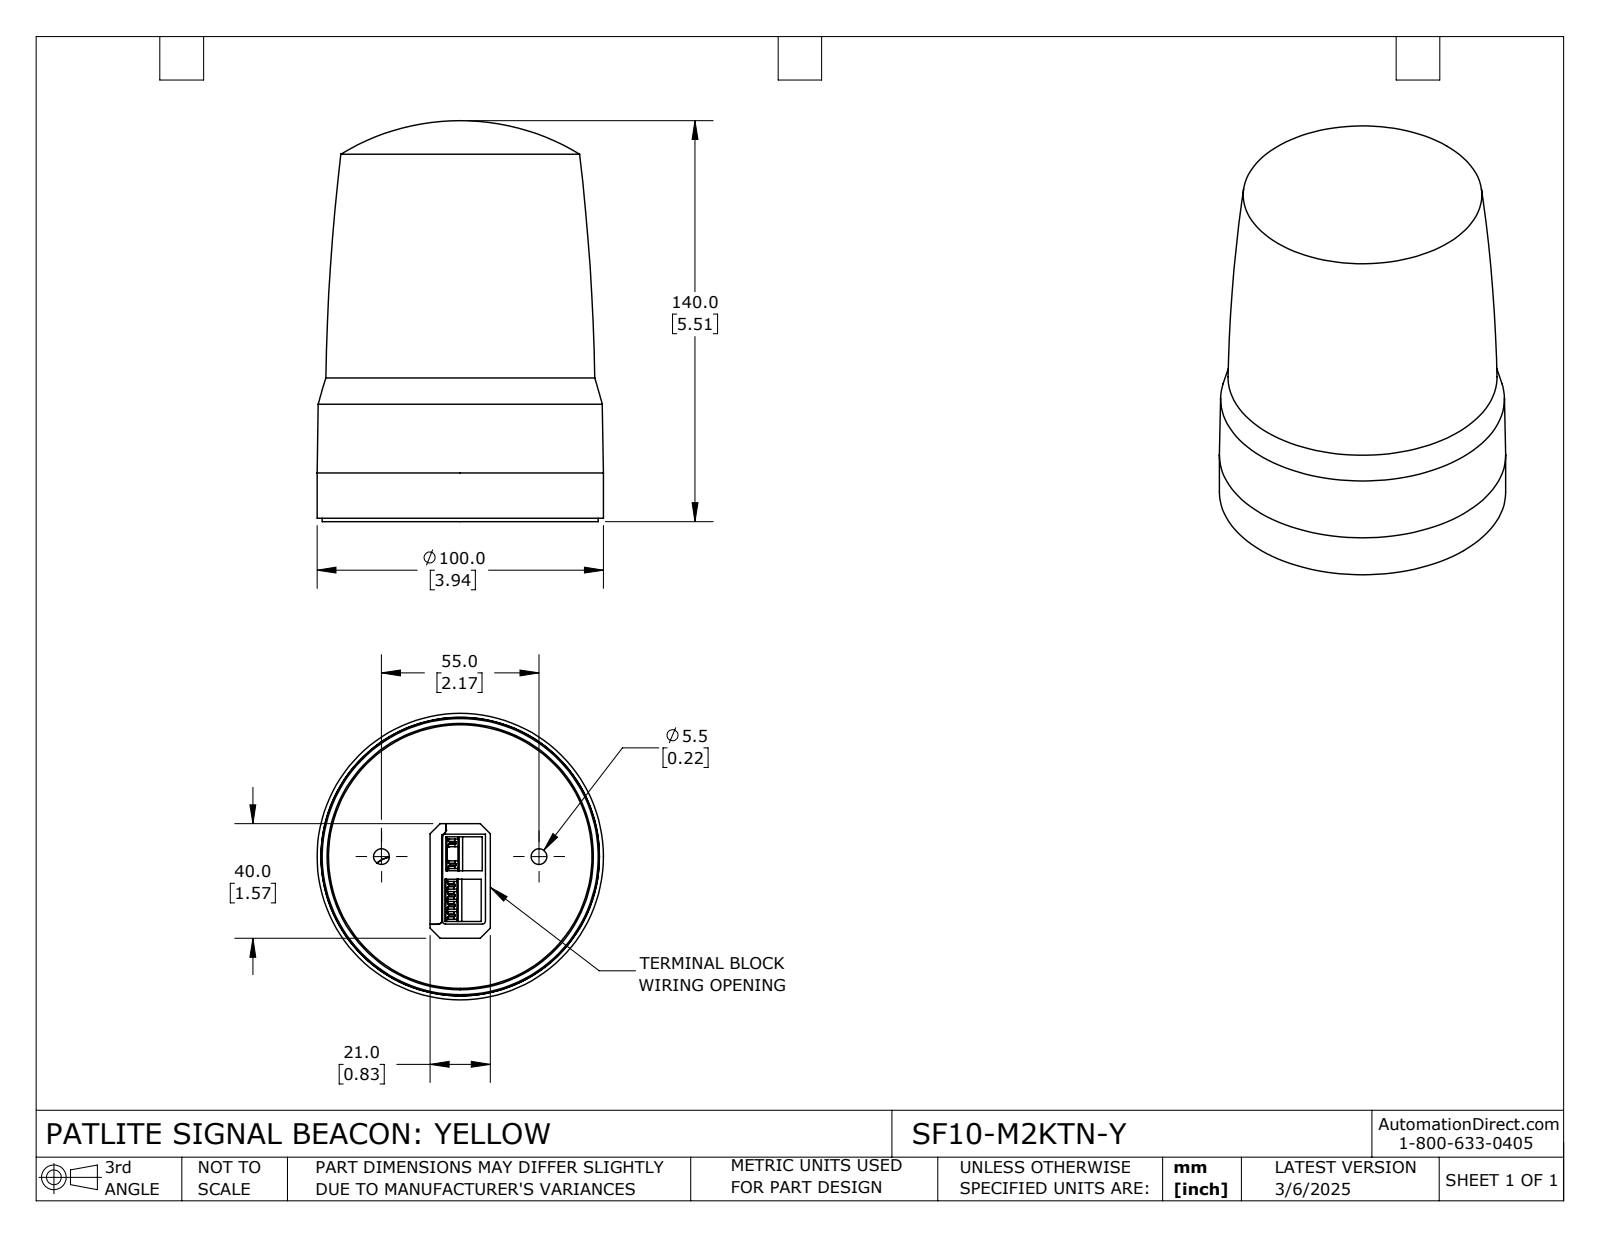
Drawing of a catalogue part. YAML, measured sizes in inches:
part_name: "SF10-M2KTN-Y"
step_written_by: "SolidWorks 2024 (CONFIG_CONTROL_DESIGN)"
units: inches
bodies: {solids: 2, faces: 268, planar: 183, cylindrical: 29, other: 56}
overall_size: [5.512, 3.937, 3.937]
volume: 52.34
surface_area: 119.3
round_holes:
  - {diameter: 0.217, count: 2}
  - {diameter: 0.512, count: 2}
  - {diameter: 3.661, count: 1}
  - {diameter: 3.764, count: 1}
round_bosses_or_shafts:
  - {diameter: 3.937, count: 1}
  - {diameter: 3.795, count: 1}
  - {diameter: 3.72, count: 1}
  - {diameter: 3.669, count: 1}
  - {diameter: 3.622, count: 1}
partial_cylinders:
  - {radius: 0.012, count: 2}
  - {radius: 1.745, count: 1}
  - {radius: 1.762, count: 1}
face_to_face_distances: [0.248, 0.579, 0.331, 0.059, 0.272, 0.52, 0.496, 0.124, 0.173, 0.276]
hole_center_spacings: [1.083, 2.165]
